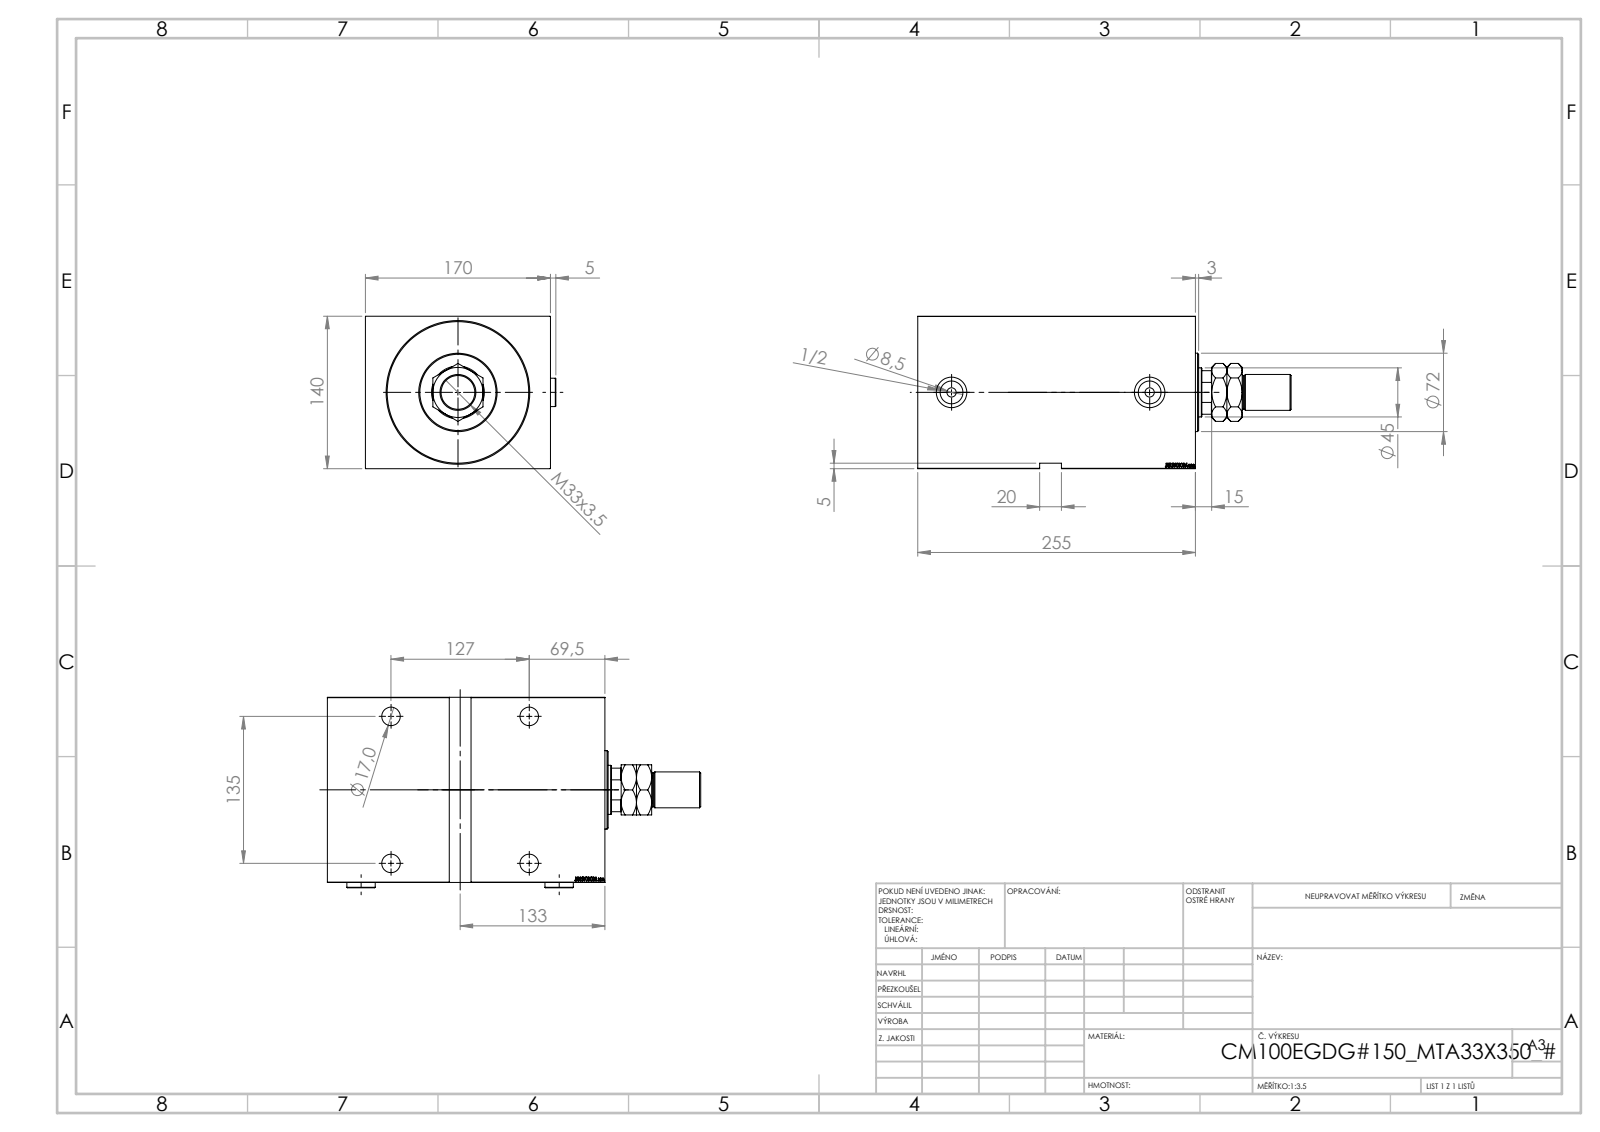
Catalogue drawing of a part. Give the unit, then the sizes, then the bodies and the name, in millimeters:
Units: millimetres
Overall size (bounding box): 343 × 174.9 × 140
Round holes (diameter × count): ⌀17 ×4, ⌀25 ×4, ⌀8.5 ×2, ⌀20.96 ×2, ⌀28 ×2, ⌀31.5 ×1, ⌀45 ×1, ⌀48.5 ×1, ⌀100 ×1, ⌀130 ×1
Round bosses / shafts (diameter × count): ⌀26 ×2, ⌀102 ×1, ⌀72 ×1, ⌀33 ×1, ⌀31 ×1
Partial cylindrical surfaces — rounded edges, fillets, slot ends (radius × count): R22 ×1
Main face-to-face distances: 140, 170, 255, 26, 229, 5, 250, 224, 90, 238.4
Hole centre spacings: 127, 135, 185.35, 182
Volume: 5 034 000 mm³ · Surface area: 428 689 mm²
Bodies: 6 solids, 961 faces (461 planar, 72 cylindrical, 428 other)
Part name (STEP PRODUCT): V450CM_E_VCP; V450CM_VC_B; MTA; V450CM_E_Body (+1 more)
STEP written by: SolidWorks 2019 (CONFIG_CONTROL_DESIGN)
